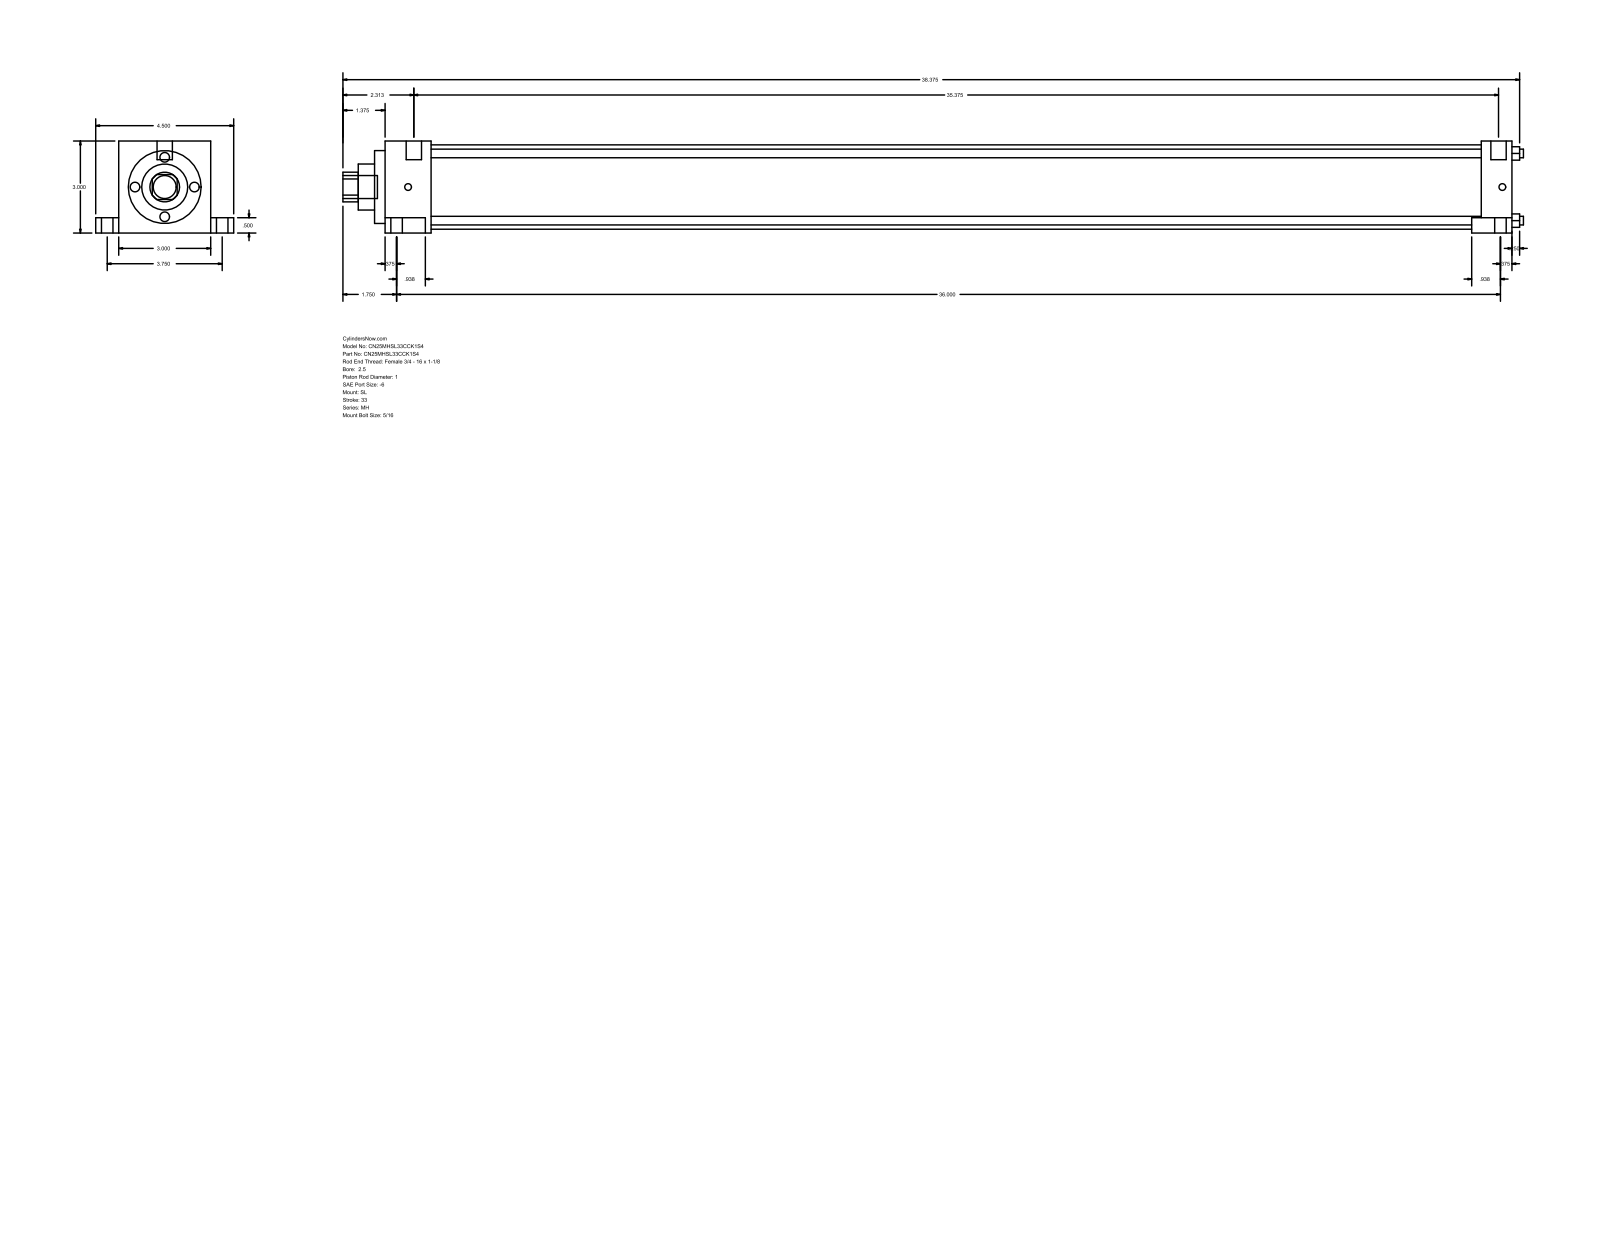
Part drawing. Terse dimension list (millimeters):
name: MH_SL__0250_1
written by: GSSL Pune (CONFIG_CONTROL_DESIGN)
unit: mm
bodies: 0 solids, 86 faces (61 planar, 25 cylindrical, 0 other)
size: 977.9 × 114.3 × 76.2
holes: 4× ⌀7.14, 1× ⌀25.4, 1× ⌀38.1, 1× ⌀60.33, 1× ⌀69.85
bosses: 2× ⌀15.88, 2× ⌀9.53, 2× ⌀5.56, 1× ⌀19.05, 1× ⌀12.7
rounds: 1× R12.29
face distances: 76.2, 25.4, 916.79, 942.19, 12.7, 63.5, 19.05, 95.25, 13.49, 930.28
hole spacings: 39.33, 55.62, 78.66
